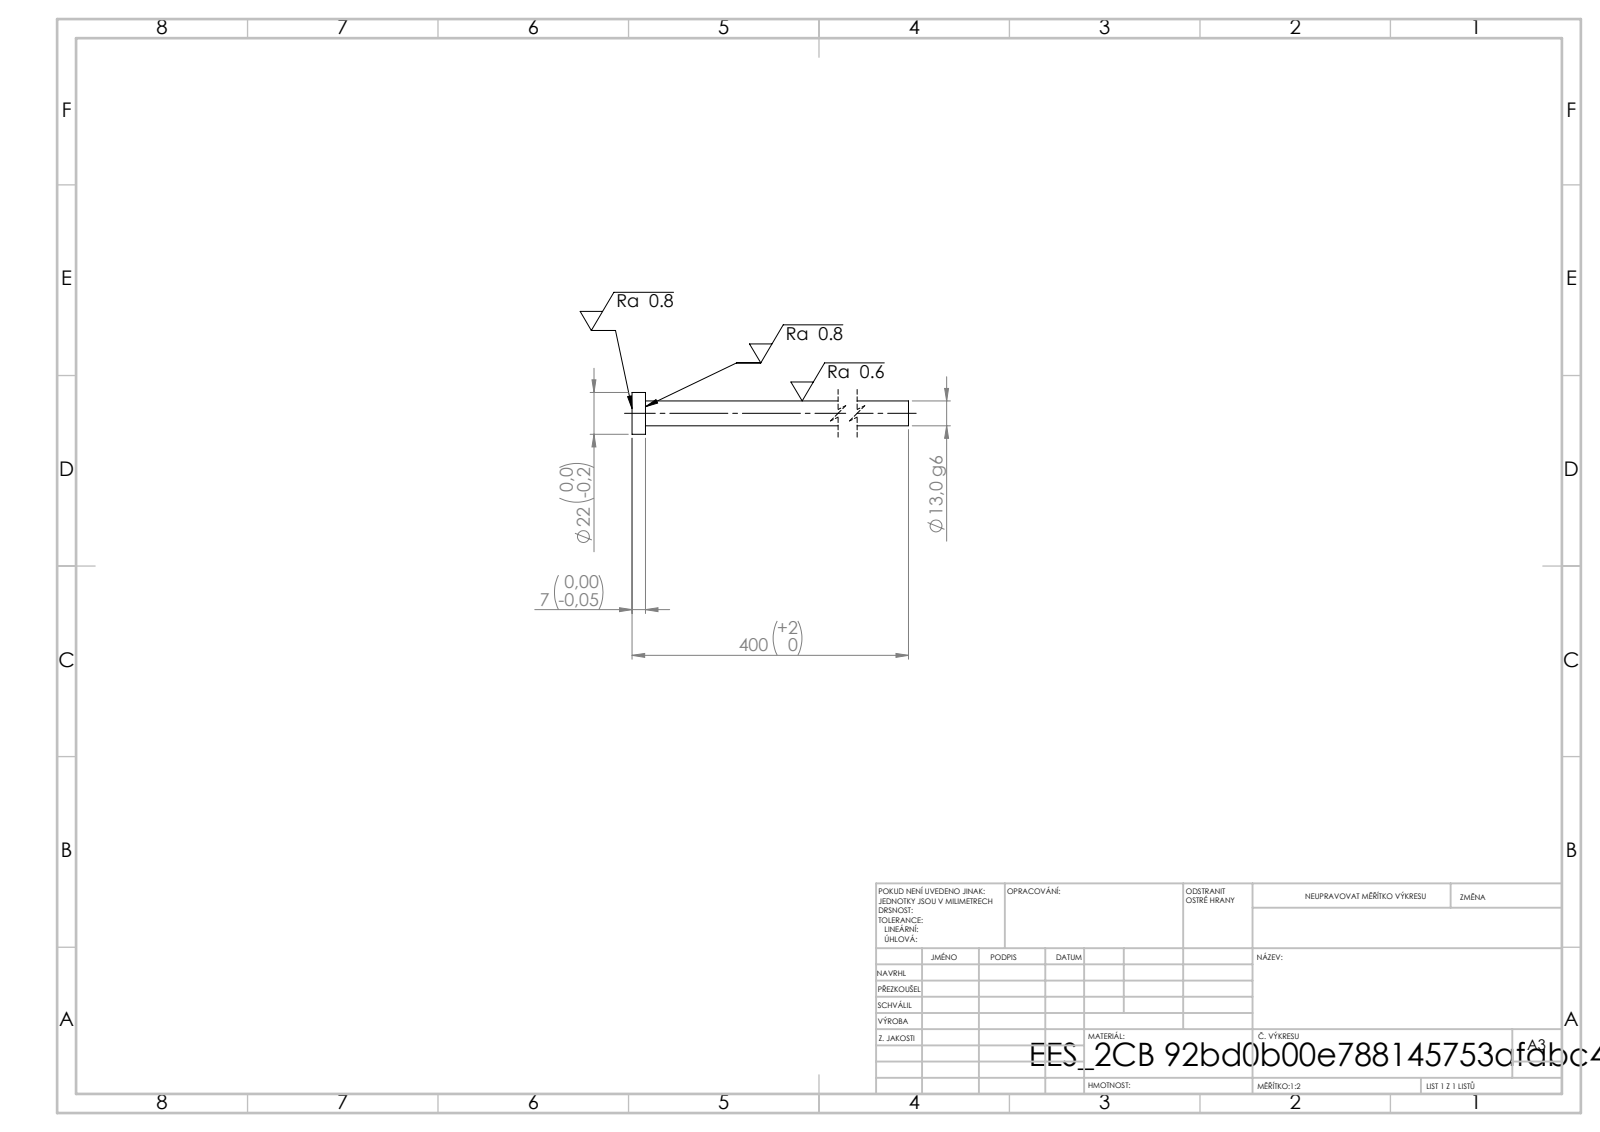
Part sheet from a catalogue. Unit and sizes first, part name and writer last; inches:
Units: inches
Overall size (bounding box): 15.748 × 0.866 × 0.866
Round bosses / shafts (diameter × count): ⌀0.866 ×1, ⌀0.512 ×1
Main face-to-face distances: 0.276, 15.748, 15.472
Volume: 3.346 in³ · Surface area: 26.81 in²
Bodies: 1 solid, 7 faces (3 planar, 4 cylindrical, 0 other)
STEP written by: SolidWorks 2019 (CONFIG_CONTROL_DESIGN)
